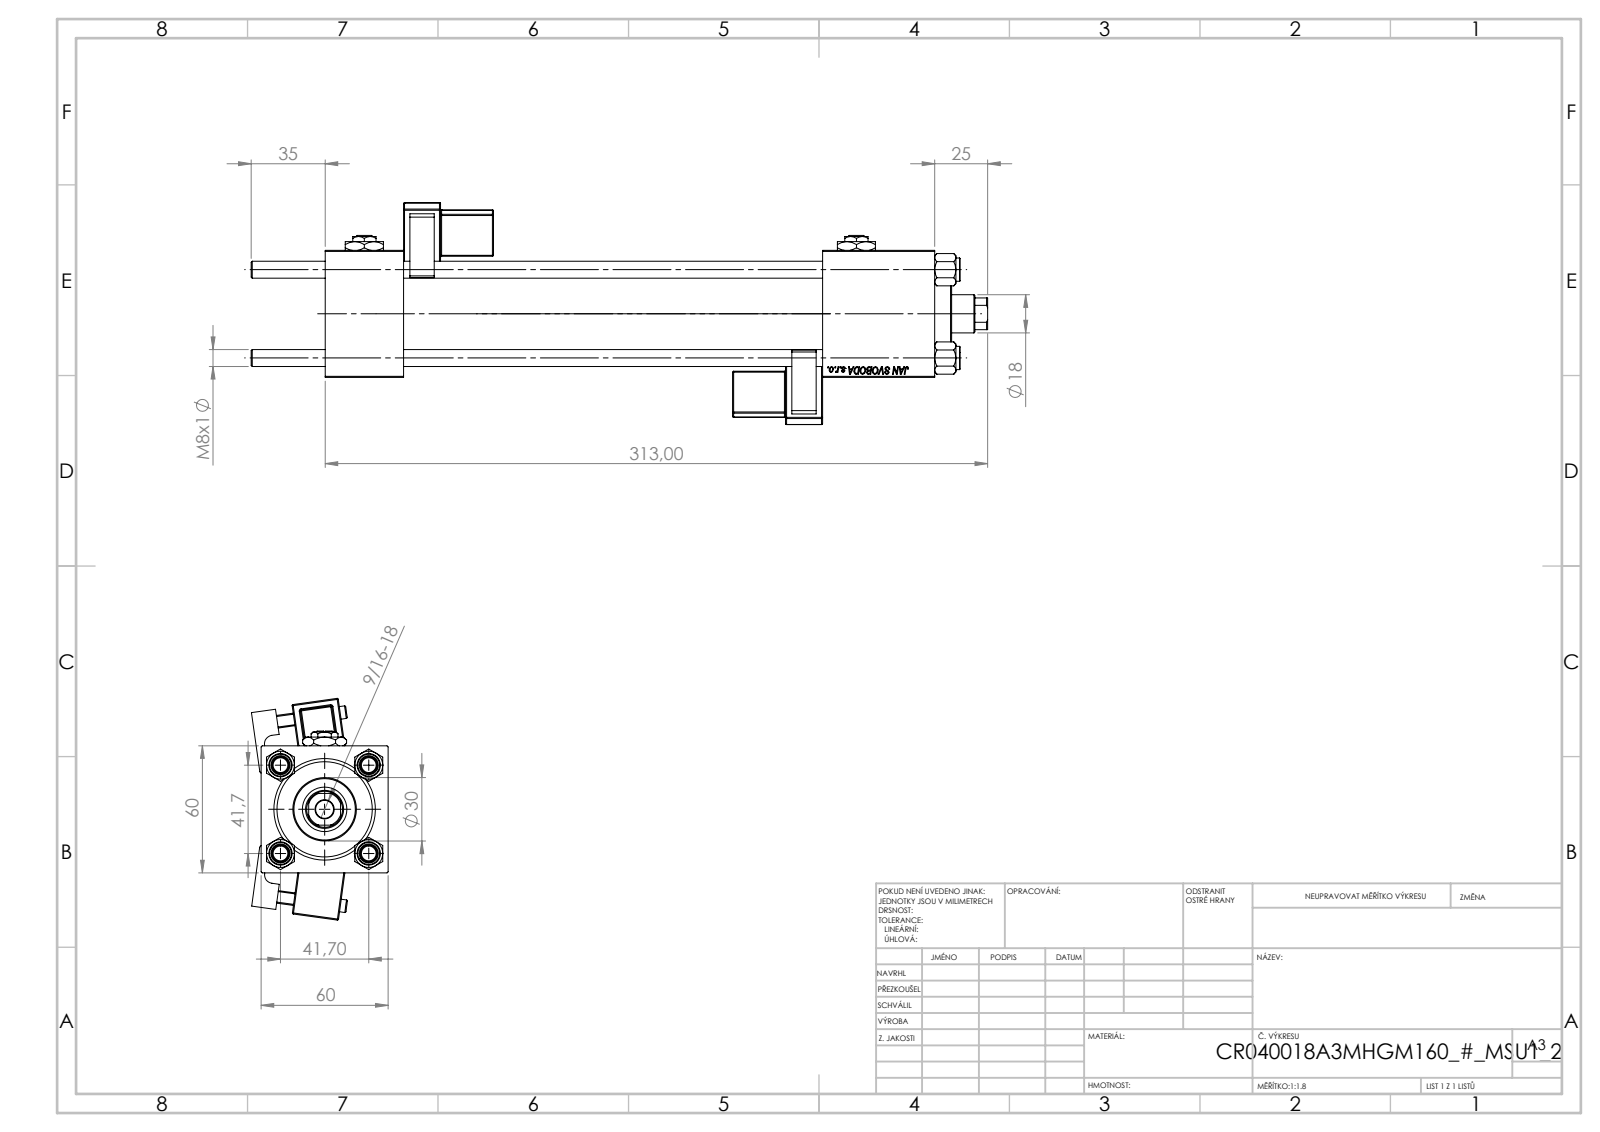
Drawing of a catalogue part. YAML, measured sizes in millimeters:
part_name: "CR025_012_A_0_G_A_G_M_020_+#_##_TYCINKA; V215CR_BODY_A; Zatka_pro_OIL_PORT; NUT_M5 (+3 more)"
step_written_by: "SolidWorks 2019 (CONFIG_CONTROL_DESIGN)"
units: millimeters
bodies: {solids: 15, faces: 1389, planar: 627, cylindrical: 148, other: 614}
overall_size: [348, 104.69, 64.58]
volume: 572001
surface_area: 188828
round_holes:
  - {diameter: 8, count: 4}
  - {diameter: 7, count: 2}
  - {diameter: 16.66, count: 2}
  - {diameter: 24, count: 2}
  - {diameter: 8.5, count: 1}
  - {diameter: 18, count: 1}
  - {diameter: 21, count: 1}
  - {diameter: 31, count: 1}
  - {diameter: 40, count: 1}
  - {diameter: 45, count: 1}
round_bosses_or_shafts:
  - {diameter: 11, count: 4}
  - {diameter: 6, count: 2}
  - {diameter: 46, count: 1}
  - {diameter: 30, count: 1}
partial_cylinders:
  - {radius: 0.5, count: 48}
  - {radius: 1, count: 2}
  - {radius: 2.5, count: 2}
  - {radius: 4, count: 2}
  - {radius: 8.5, count: 1}
face_to_face_distances: [60, 37, 53, 288, 251, 235, 198, 259.3, 222.3, 24.3]
hole_center_spacings: [29.49, 41.7, 58.97, 232.5]
